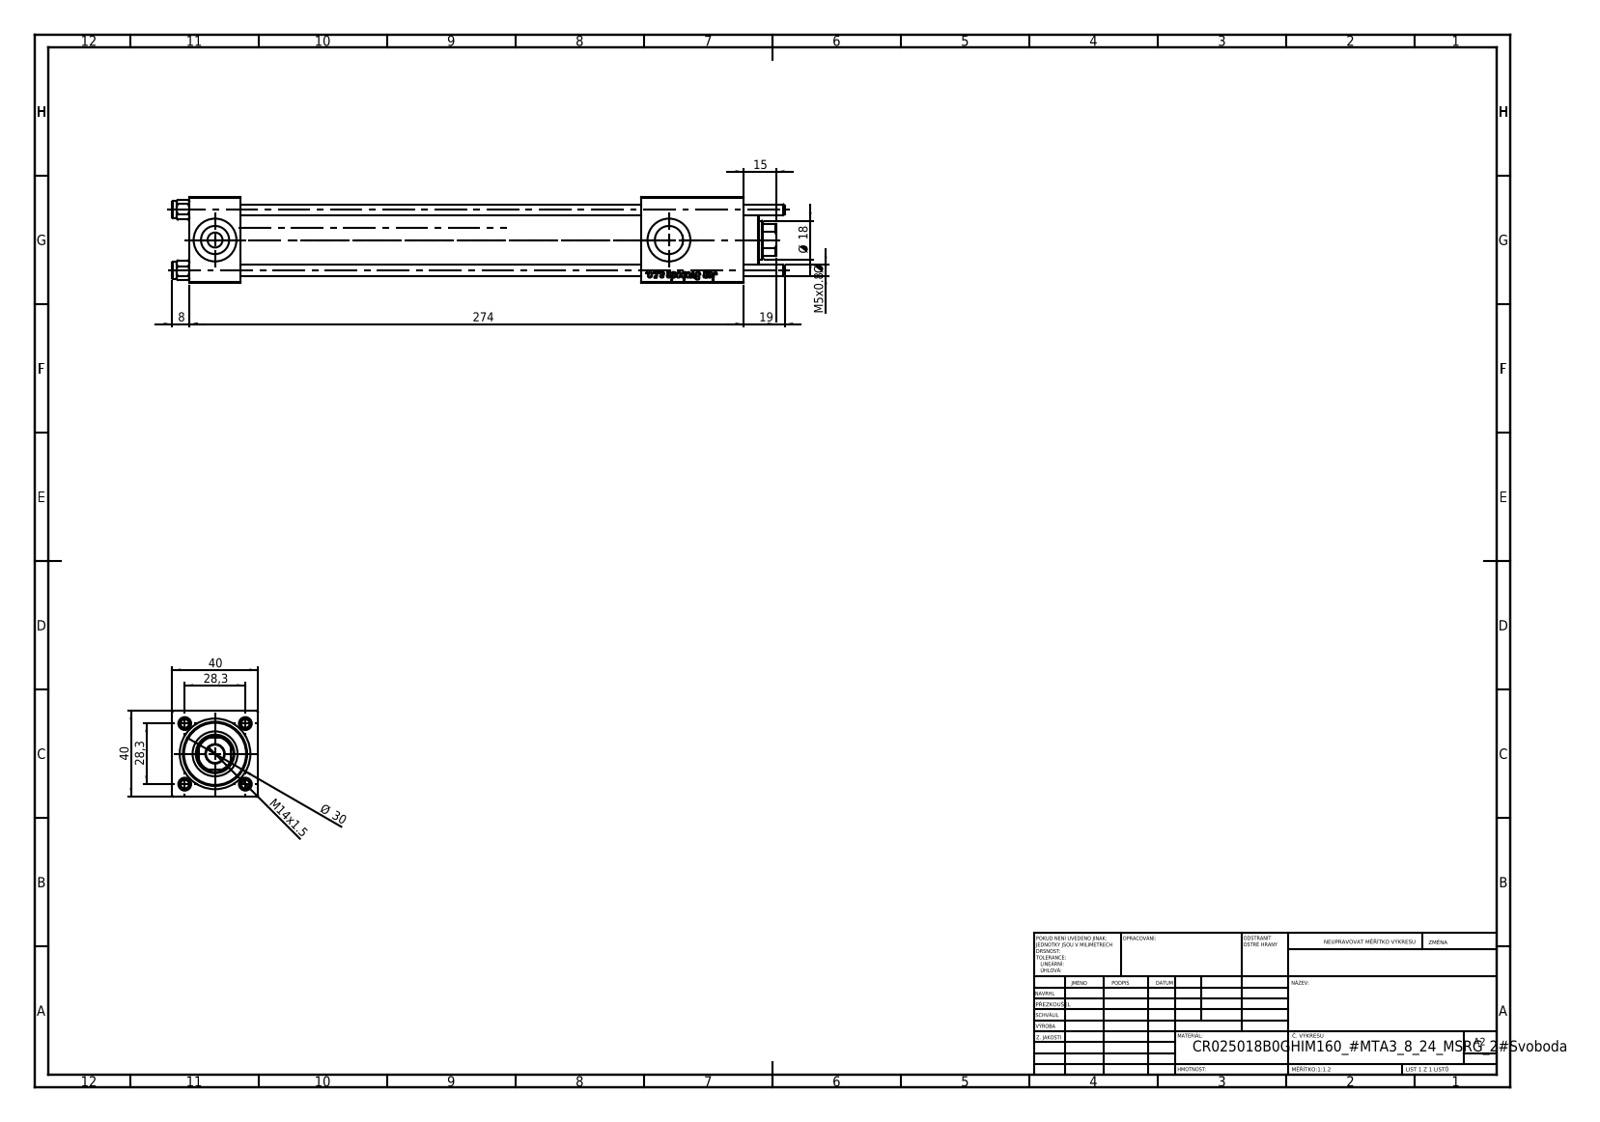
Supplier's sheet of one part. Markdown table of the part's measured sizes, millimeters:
| quantity | value |
| --- | --- |
| part name | V215CR_B_TYCINKA; V215_VC_A; V215CR_B-1; NUT_M5_B (+1 more) |
| STEP written by | SolidWorks 2019 (CONFIG_CONTROL_DESIGN) |
| units | millimeters |
| bodies | 11 solids, 1152 faces (428 planar, 76 cylindrical, 648 other) |
| overall size | 286 × 40 × 40 |
| volume | 236 057 mm³ |
| surface area | 102 238 mm² |
| round holes (diameter × count) | 5 × 4, 20 × 3, 7 × 2, 13.16 × 2, 8.5 × 1, 18 × 1, 21 × 1, 25 × 1, 30 × 1 |
| round bosses / shafts (diameter × count) | 8 × 4, 31 × 1 |
| partial cylindrical surfaces (radius × count) | 8.5 × 1 |
| main face-to-face distances | 40, 24, 211, 187, 230.3, 206.3, 19.3, 259, 235, 48 |
| hole center spacings | 20.01, 28.3, 40.02, 212 |
